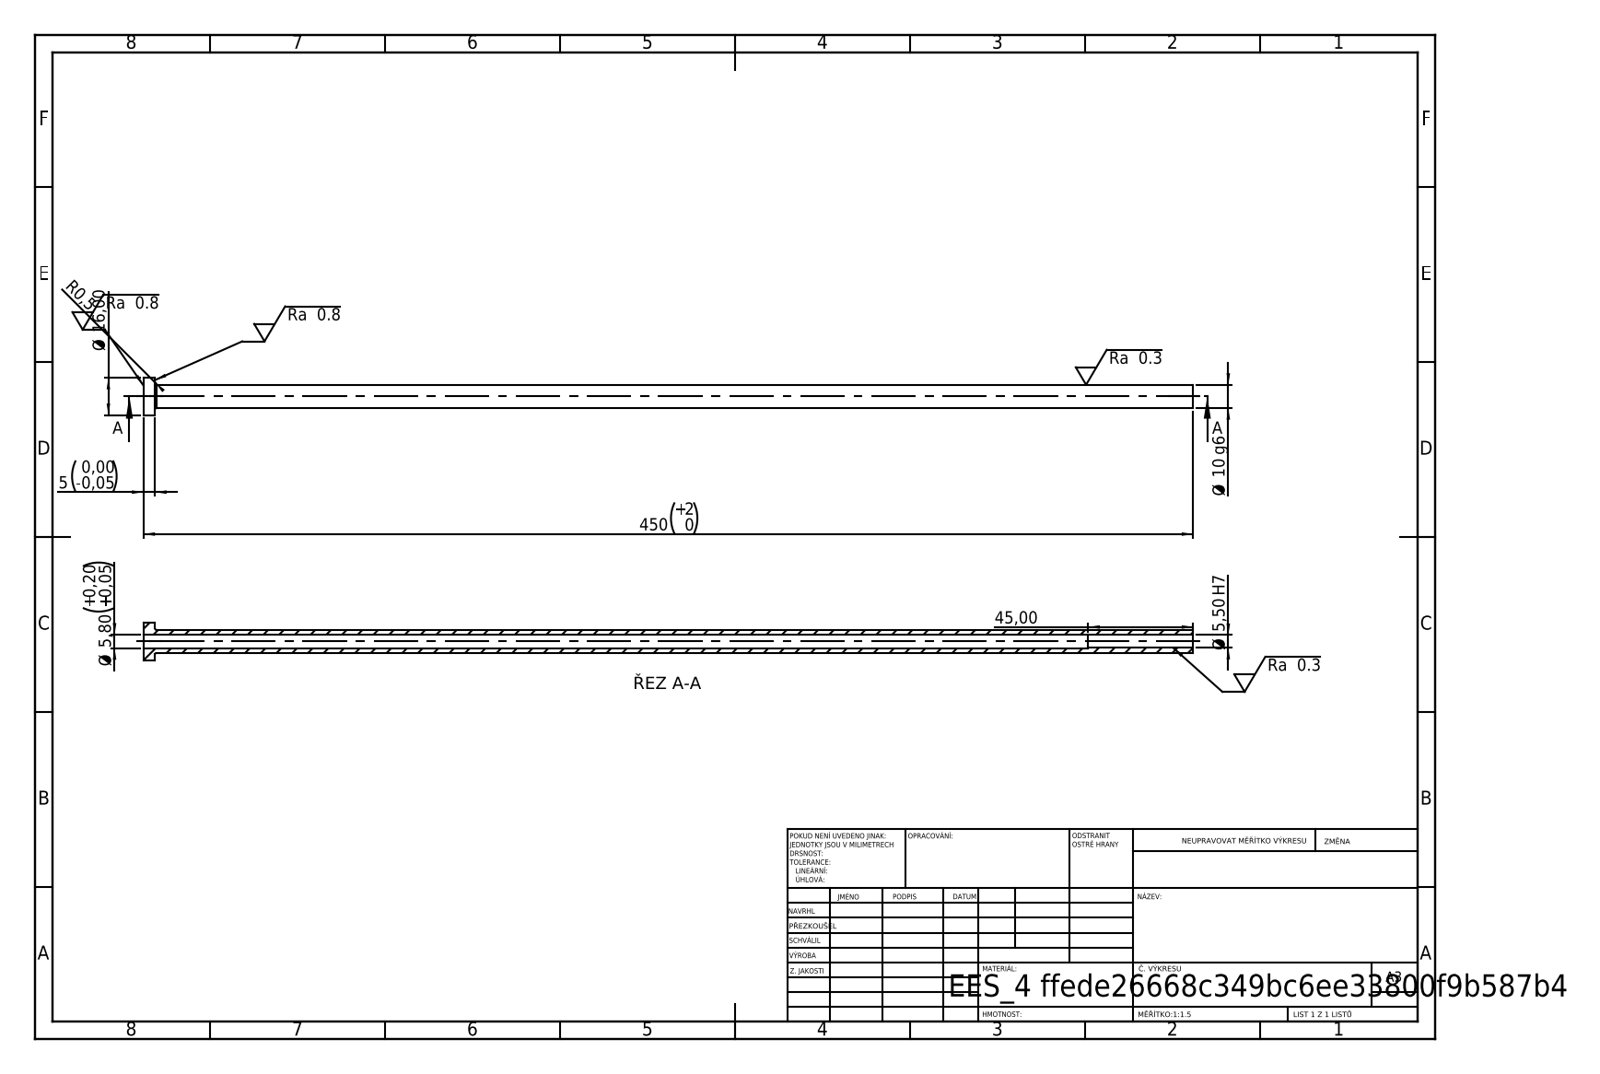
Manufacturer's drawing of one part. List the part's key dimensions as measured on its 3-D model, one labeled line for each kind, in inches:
STEP written by: SolidWorks 2019 (CONFIG_CONTROL_DESIGN)
Units: inches
Bodies: 1 solid, 14 faces (4 planar, 8 cylindrical, 2 other)
Overall size (bounding box): 17.717 × 0.63 × 0.63
Volume: 1.476 in³ · Surface area: 35.24 in²
Round holes (diameter × count): ⌀0.217 ×1, ⌀0.228 ×1
Round bosses / shafts (diameter × count): ⌀0.63 ×1, ⌀0.394 ×1
Main face-to-face distances: 0.197, 17.717, 17.52, 15.945, 15.748, 1.772
